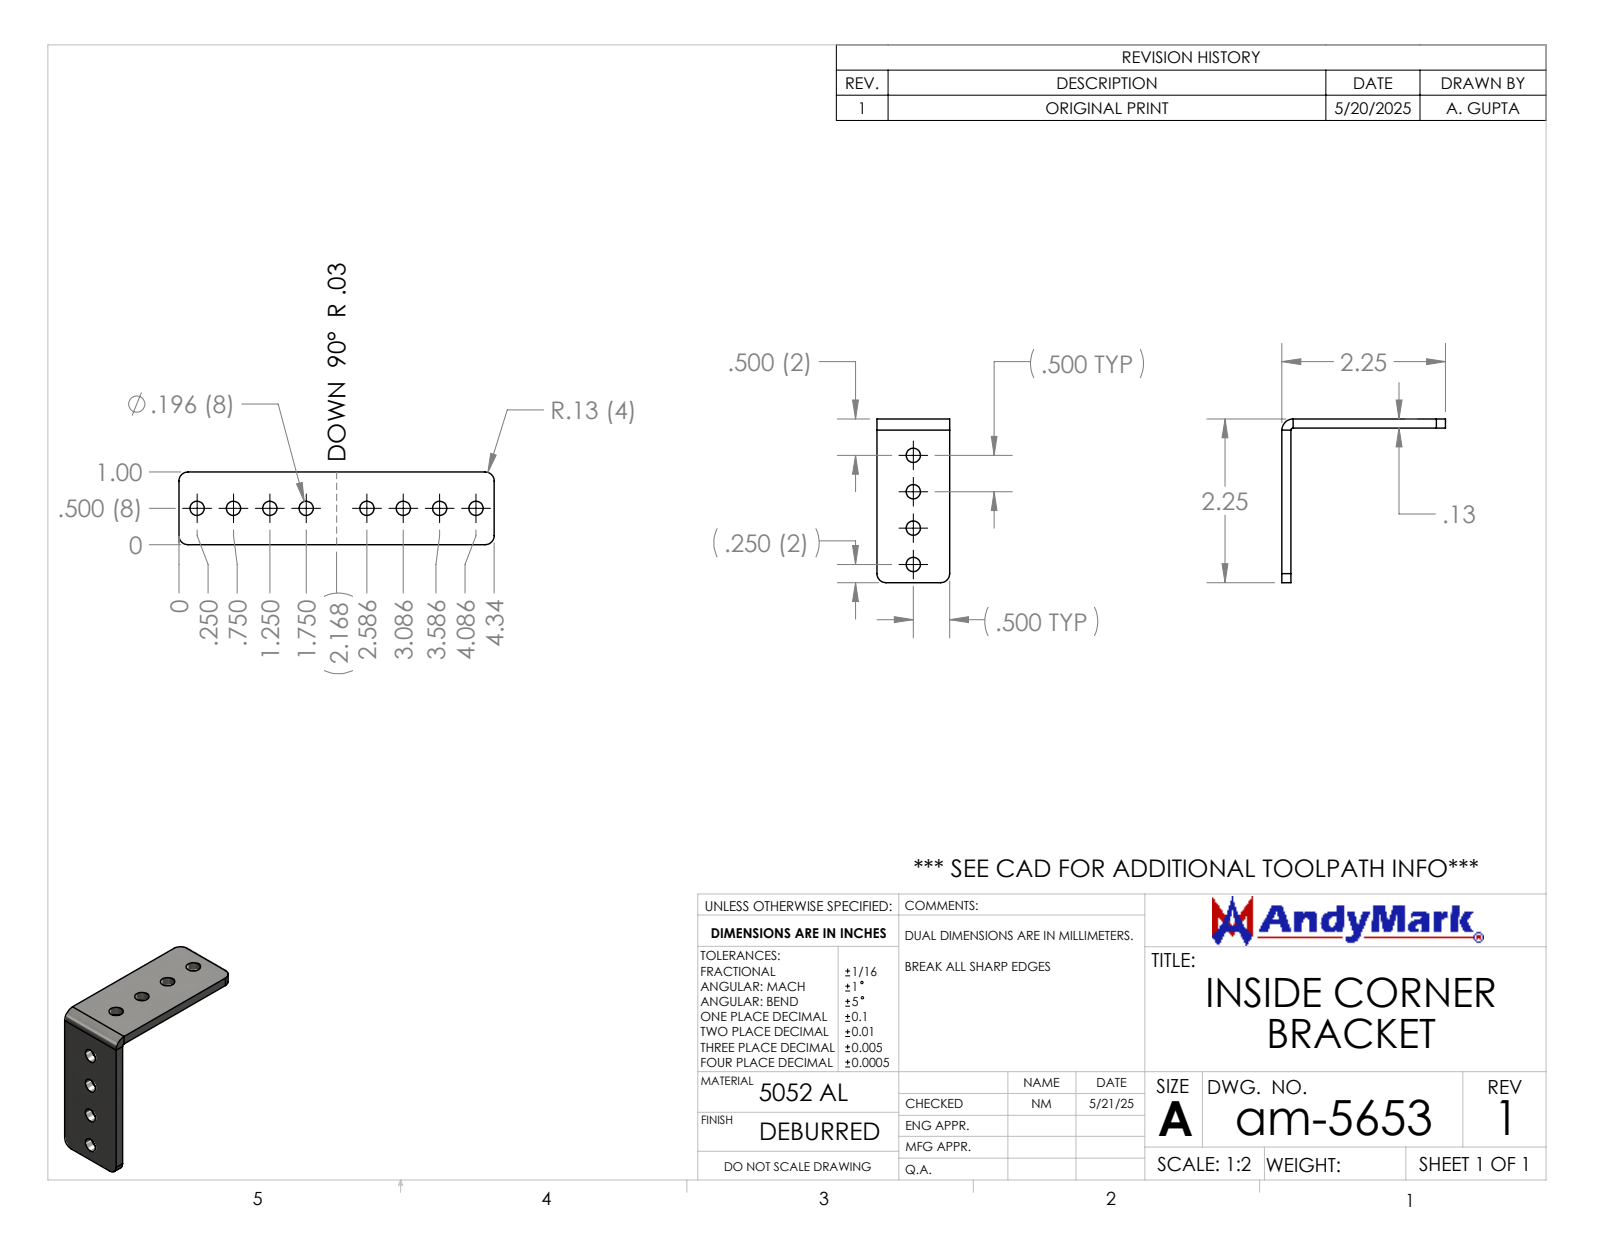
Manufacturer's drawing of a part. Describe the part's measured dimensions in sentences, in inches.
The part is named "Inside Corner Bracket". Its 3-D file was written by "SolidWorks 2024 (AUTOMOTIVE_DESIGN)". It is 1 solid with 34 faces: 12 planar, 22 cylindrical and 0 other. Overall it measures 2.25 by 2.25 by 1 inches. Its volume is 0.51 cubic inches and its surface area 10.08 square inches. Round holes: 8 of diameter 0.196. Partial cylindrical surfaces (rounded edges, fillets, slot ends): 4 of radius 0.125, 1 of radius 0.029, 1 of radius 0.154. The main face-to-face distances are 0.125, 0.125, 1, 2.25, 2.125, 2.125. The hole center spacings are 0.5, 1, 1.5.
